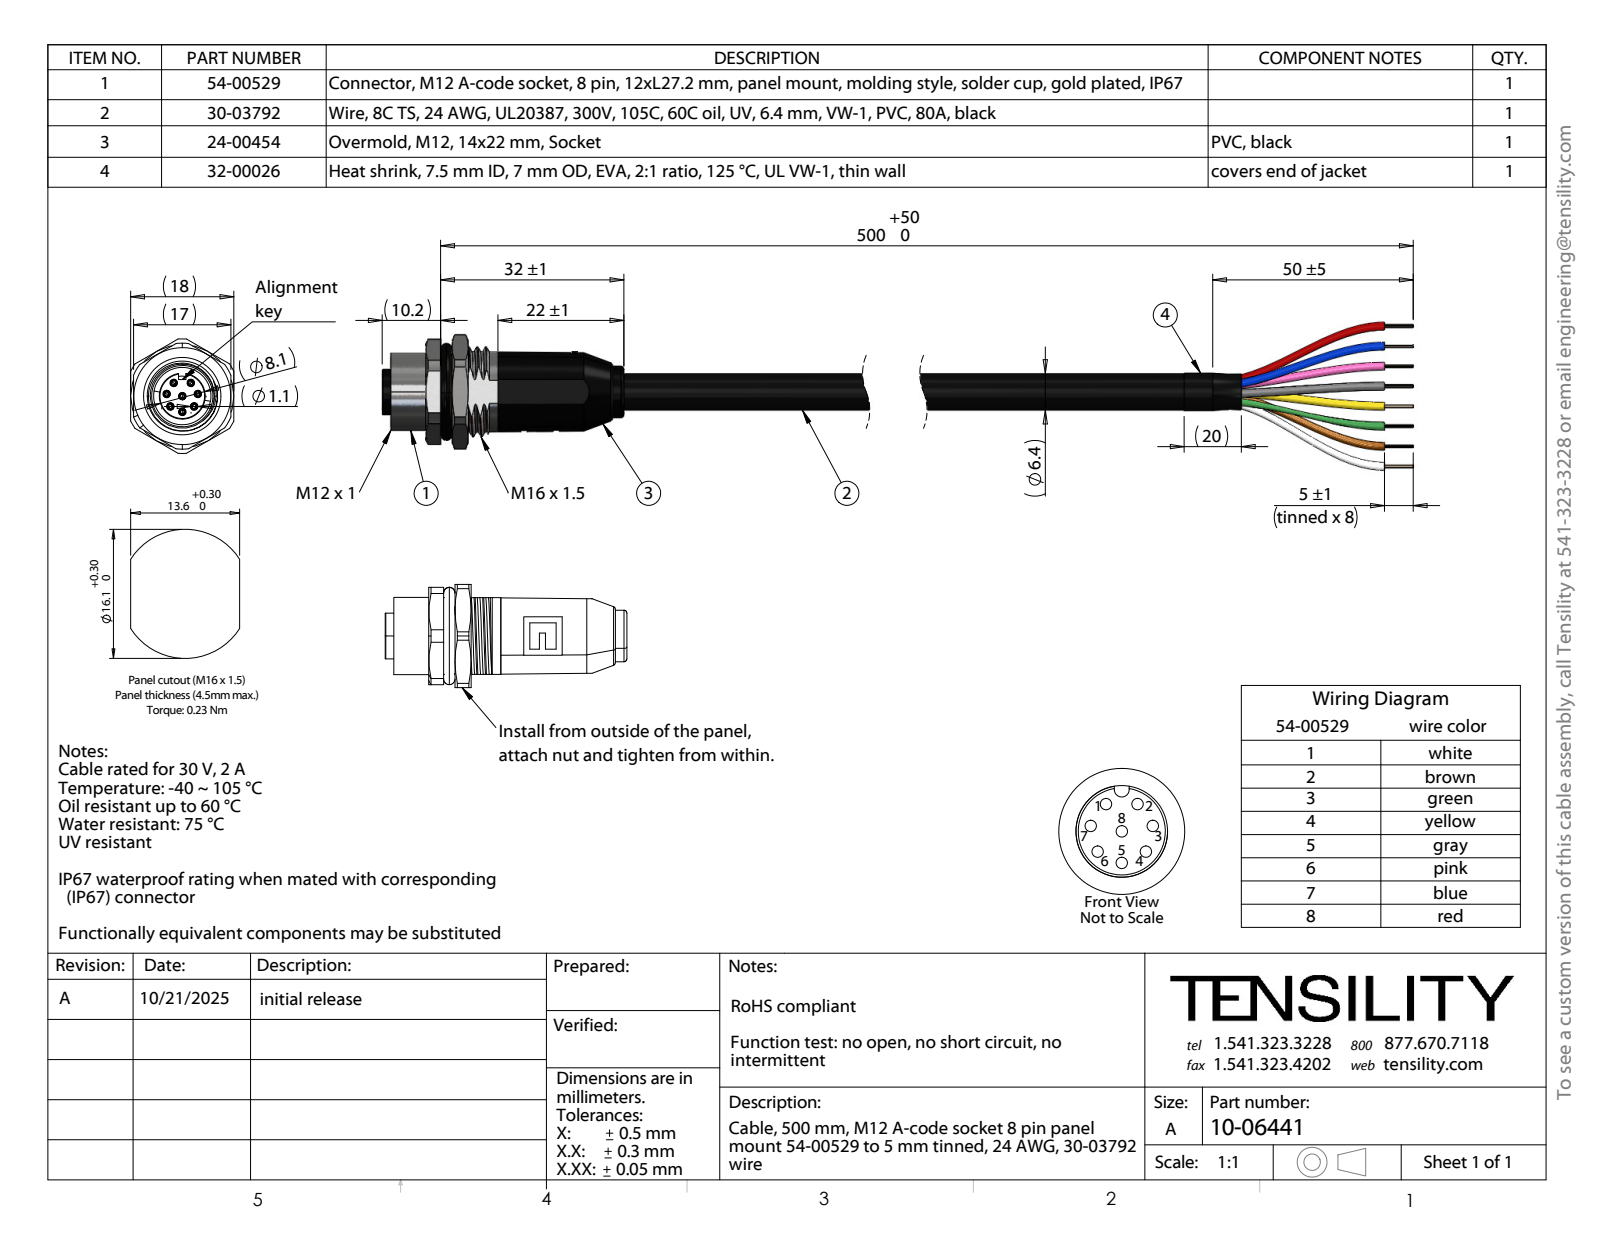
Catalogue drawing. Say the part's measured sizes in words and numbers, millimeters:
The part is named "10-06441; 24-00454; 30-03792_50mm; 32-00026_10 mm (+2 more)". Its 3-D file was written by "SolidWorks 2025 (CONFIG_CONTROL_DESIGN)". It is 336 solids with 2190 faces: 893 planar, 967 cylindrical and 330 other. Overall it measures 227.2 by 25.9 by 18 millimeters. Its volume is 11 135 cubic millimeters and its surface area 12 480 square millimeters. Round holes: 8 of diameter 1.2, 8 of diameter 1.3, 8 of diameter 1.6, 1 of diameter 7.5, 1 of diameter 8.8, 1 of diameter 9.1, 1 of diameter 9.6, 1 of diameter 11.2, 1 of diameter 12.2, 1 of diameter 14.7. Round bosses or shafts: 8 of diameter 1.7, 8 of diameter 1.56, 8 of diameter 1.52, 1 of diameter 13.95, 1 of diameter 13.5, 1 of diameter 12.5, 1 of diameter 11, 1 of diameter 10.7. Partial cylindrical surfaces (rounded edges, fillets, slot ends): 8 of radius 0.5, 1 of radius 7.04, 1 of radius 7.9, 1 of radius 9.25, 1 of radius 10. The main face-to-face distances are 0.5, 2, 10, 1.5, 2.6, 11.5, 18, 9.5, 8, 17.5. The hole center spacings are 2.75, 4.15, 2.27, 2.28, 2.29, 4.64, 5.27, 5.28.
